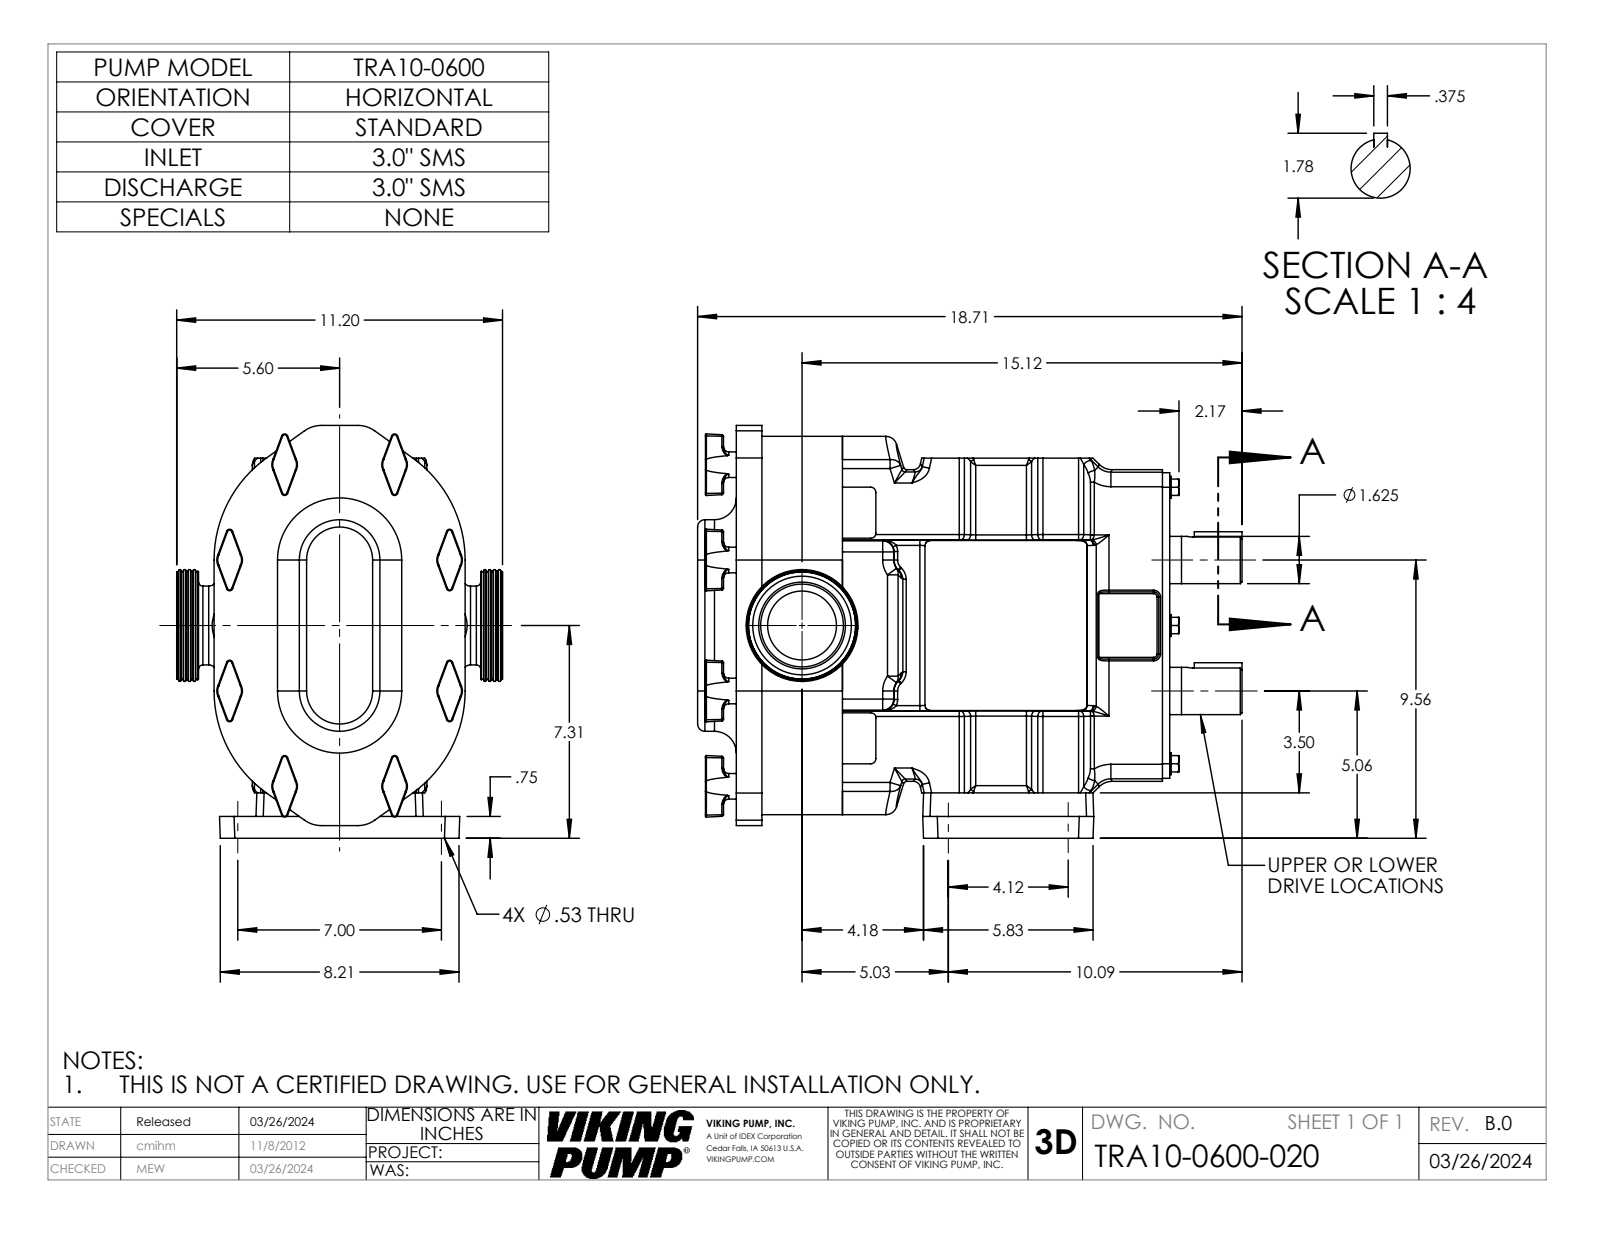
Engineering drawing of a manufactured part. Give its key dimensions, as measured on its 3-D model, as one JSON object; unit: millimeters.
{"part_name": "TRA10-0600-COVER-STD; TRA10-0600-BODY; TRA10-0600-GEARBOX-H; 0600SMS30 (+1 more)", "step_written_by": "SolidWorks 2022 (AUTOMOTIVE_DESIGN)", "units": "millimeters", "bodies": {"solids": 5, "faces": 1141, "planar": 289, "cylindrical": 376, "other": 476}, "overall_size": [475.3, 360.3, 284.5], "volume_mm3": 19520000, "surface_area_mm2": 886400, "round_holes": [[13.5, 4], [60.1, 1], [72.3, 1], [86.1, 1]], "round_bosses_or_shafts": [[22.4, 8], [19.1, 6], [41.2, 2], [75.7, 1], [68.8, 1]], "partial_cylinders_radius": [[4.6, 44], [1.5, 43], [0.8, 32], [6.4, 32], [9.7, 28], [3, 24], [12.7, 20], [9.5, 12]], "face_to_face_distances": [70.3, 12.7, 22.4, 92.7, 9.1, 378.4, 356.1, 285.8, 165.1, 21.8], "hole_center_spacings": [104.6, 177.8, 206.3]}
